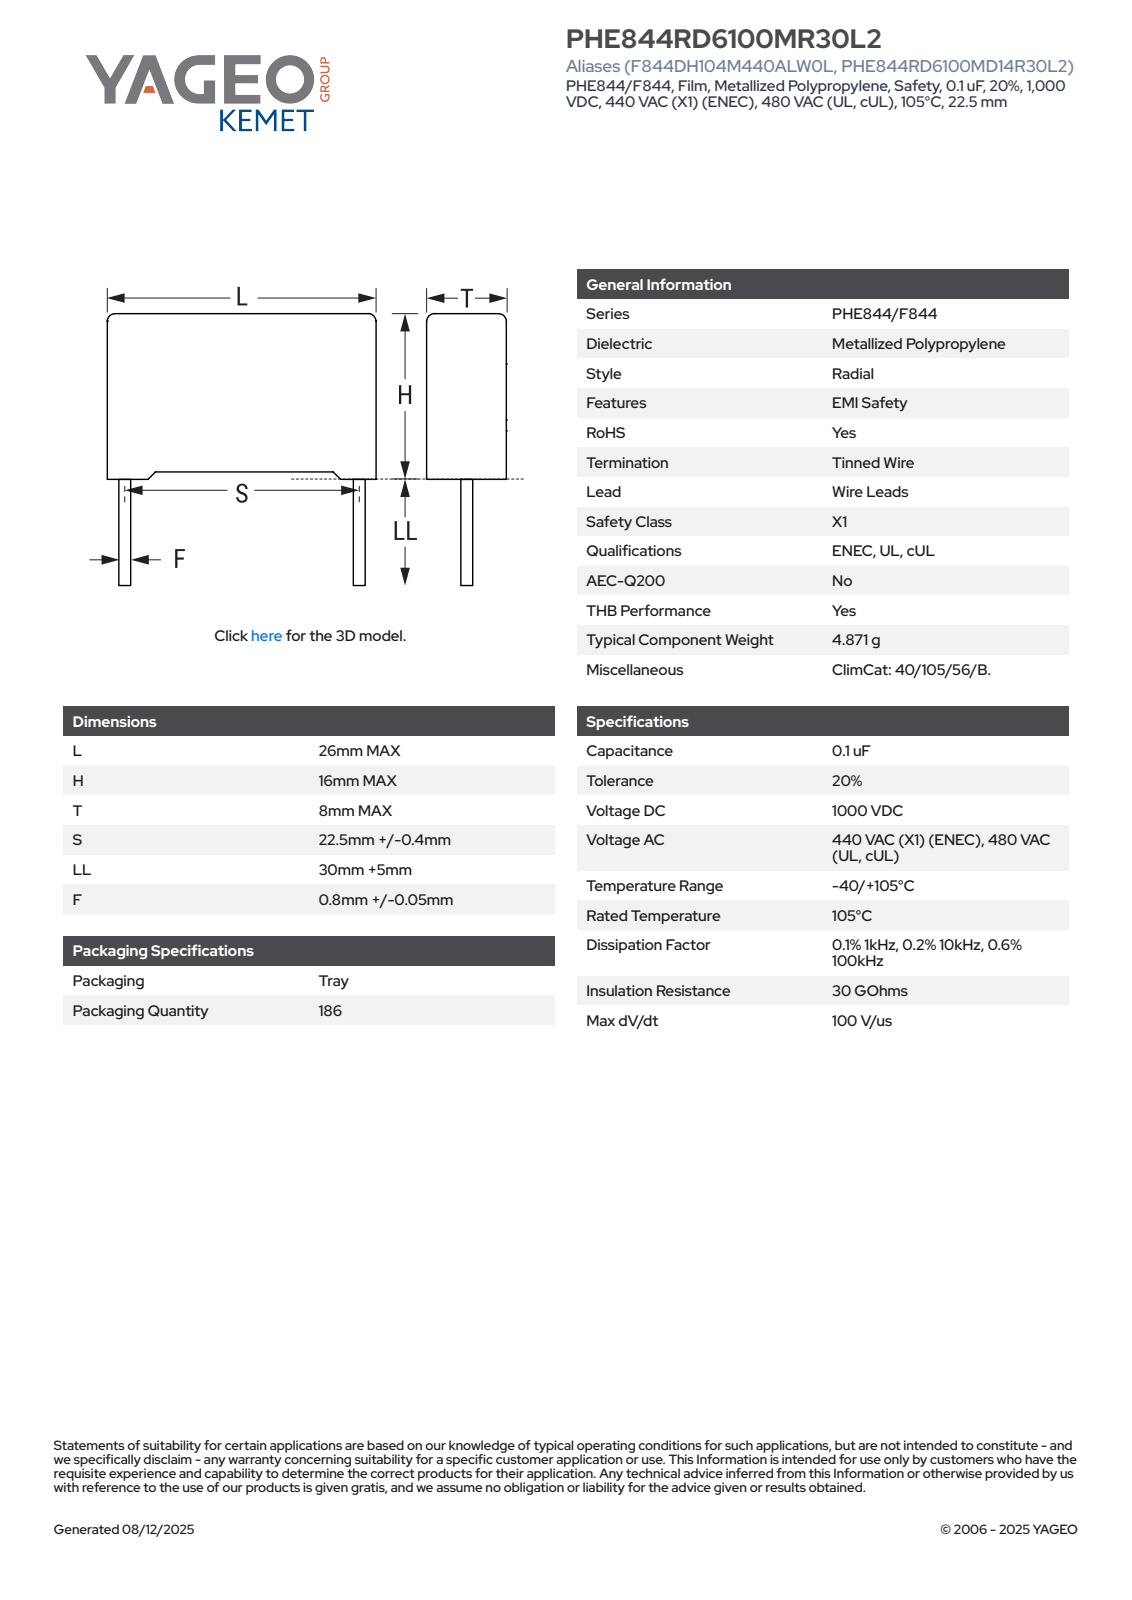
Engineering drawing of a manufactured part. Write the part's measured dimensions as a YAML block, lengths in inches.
part_name: "CFR_RB2_26X16X8_L26H16T8S22.5LL35F0.85"
step_written_by: "SolidWorks 2021 (AUTOMOTIVE_DESIGN)"
units: inches
bodies: {solids: 4, faces: 85, planar: 77, cylindrical: 8, other: 0}
overall_size: [2.008, 1.024, 0.315]
volume: 0.197
surface_area: 2.691
round_bosses_or_shafts:
  - {diameter: 0.033, count: 2}
partial_cylinders:
  - {radius: 0.02, count: 4}
face_to_face_distances: [0.315, 0.6, 1.024, 0.608, 0.034, 0.022, 0.03, 0.63, 0.281, 0.315]
